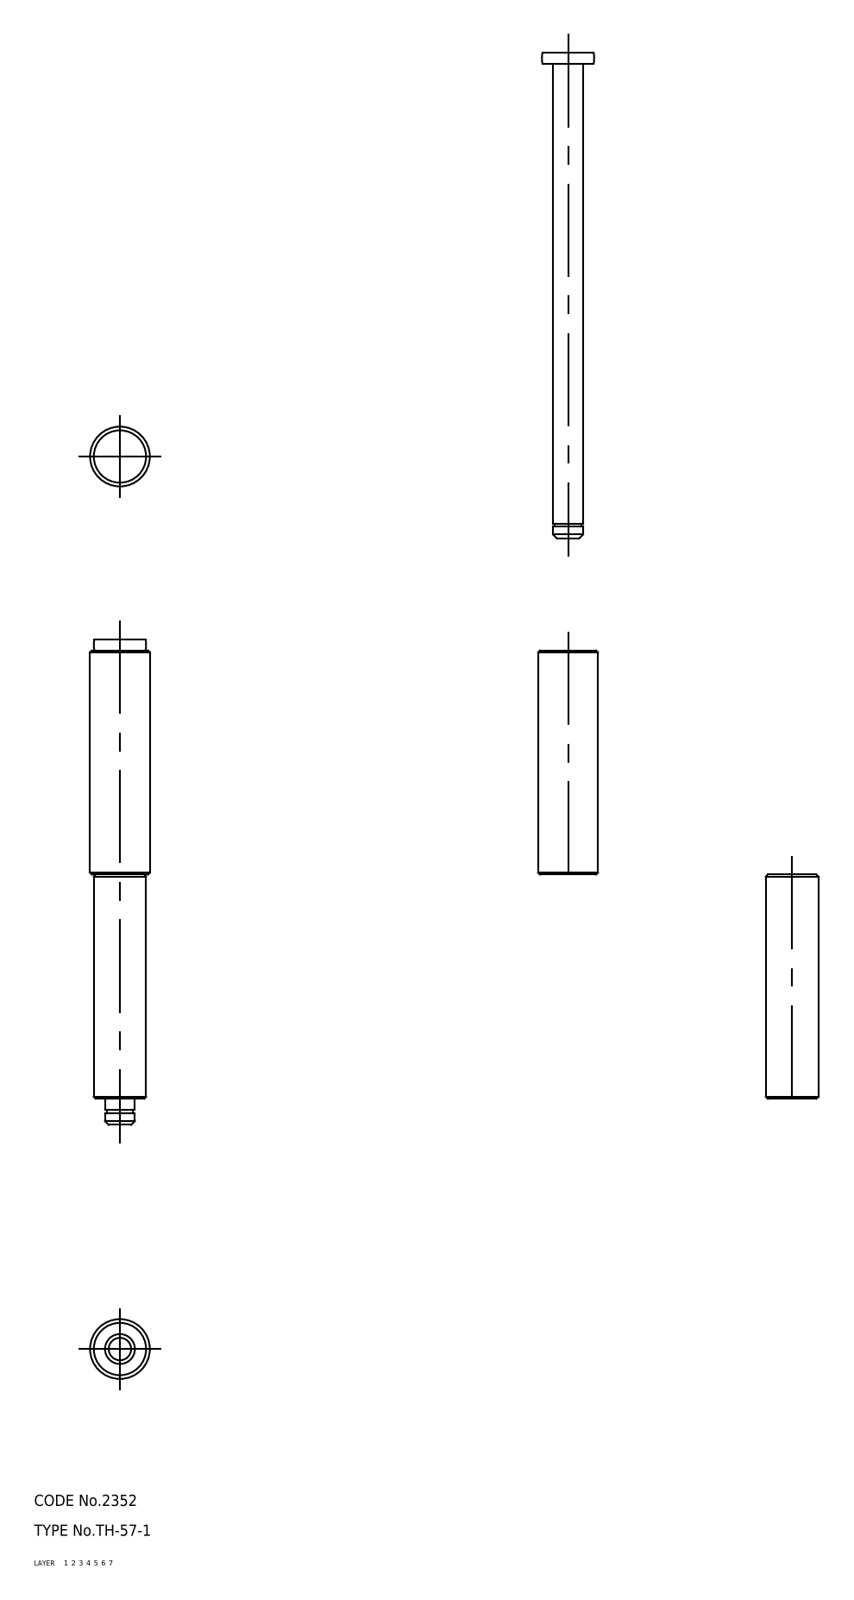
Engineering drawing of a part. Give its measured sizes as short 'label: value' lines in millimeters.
name: shaft; collar_B; collar_A; TH_57_1_11576_36
written by: CADfix (AUTOMOTIVE_DESIGN)
unit: mm
bodies: 3 solids, 34 faces (0 planar, 0 cylindrical, 34 other)
size: 130 × 16 × 16
volume: 22 102 mm³; area: 12 754 mm²
